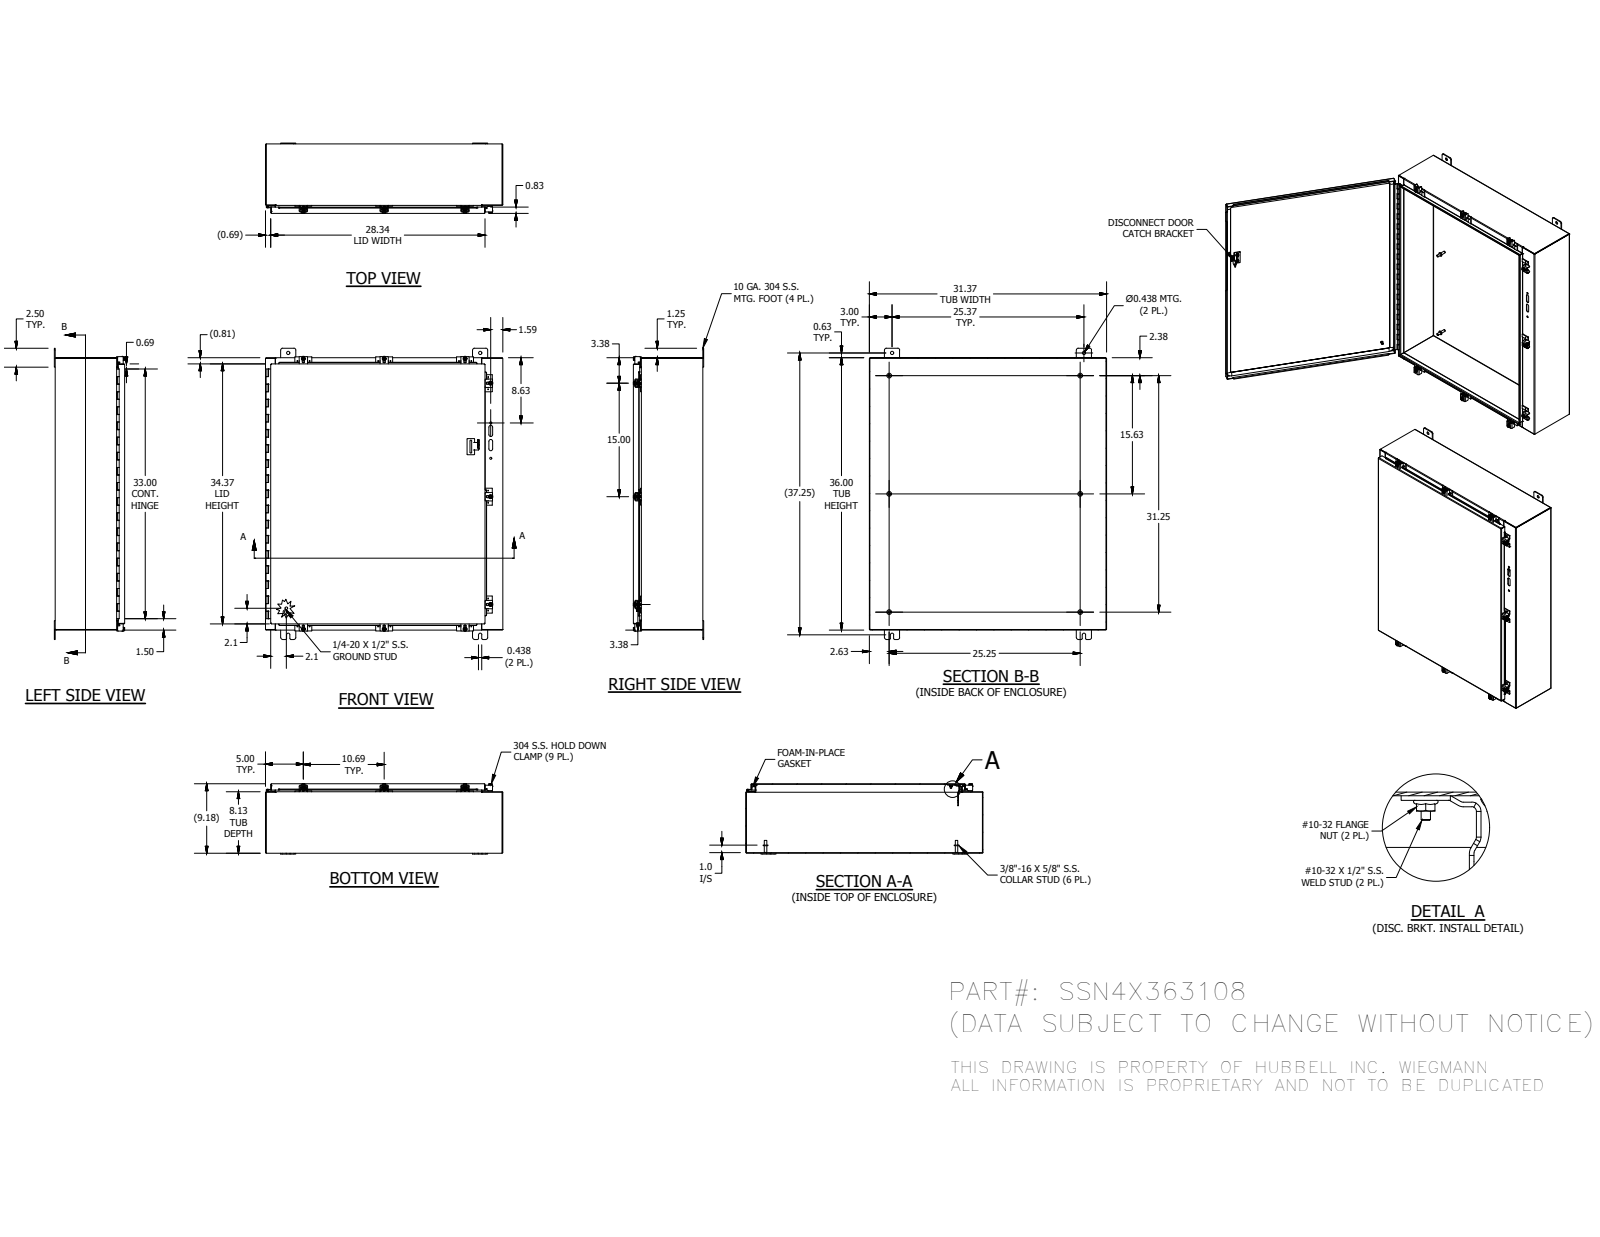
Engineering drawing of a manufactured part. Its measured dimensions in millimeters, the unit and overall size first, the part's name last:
Units: millimetres
Overall size (bounding box): 977.9 × 796.92 × 236.25
Round holes (diameter × count): ⌀2.79 ×18, ⌀5.36 ×9, ⌀7.16 ×9, ⌀11.13 ×4, ⌀3.17 ×2, ⌀3.96 ×2, ⌀7.14 ×2
Round bosses / shafts (diameter × count): ⌀15.88 ×15, ⌀6.35 ×11, ⌀13.21 ×9, ⌀8.89 ×9, ⌀5.04 ×9, ⌀8.38 ×6, ⌀0.76 ×4, ⌀8.56 ×3
Partial cylindrical surfaces — rounded edges, fillets, slot ends (radius × count): R0.76 ×73, R6.35 ×39, R0.79 ×27, R2.67 ×23, R3.17 ×23, R3.62 ×18, R0.38 ×13, R1.59 ×13
Main face-to-face distances: 1.88, 231.19, 229.31, 233.07, 912.52, 1.87, 204.5, 26.69, 796.92, 795.04
Hole centre spacings: 899.74, 22.26, 271.46, 292.22, 931.59, 933.82, 945.74, 250.96
Volume: 4 918 000 mm³ · Surface area: 5 027 000 mm²
Bodies: 58 solids, 2046 faces (1040 planar, 580 cylindrical, 426 other)
Part name (STEP PRODUCT): SSN4X363108BKP; 38859; 34871; 328140L (+8 more)
STEP written by: Autodesk Inventor 2016 (AUTOMOTIVE_DESIGN)
